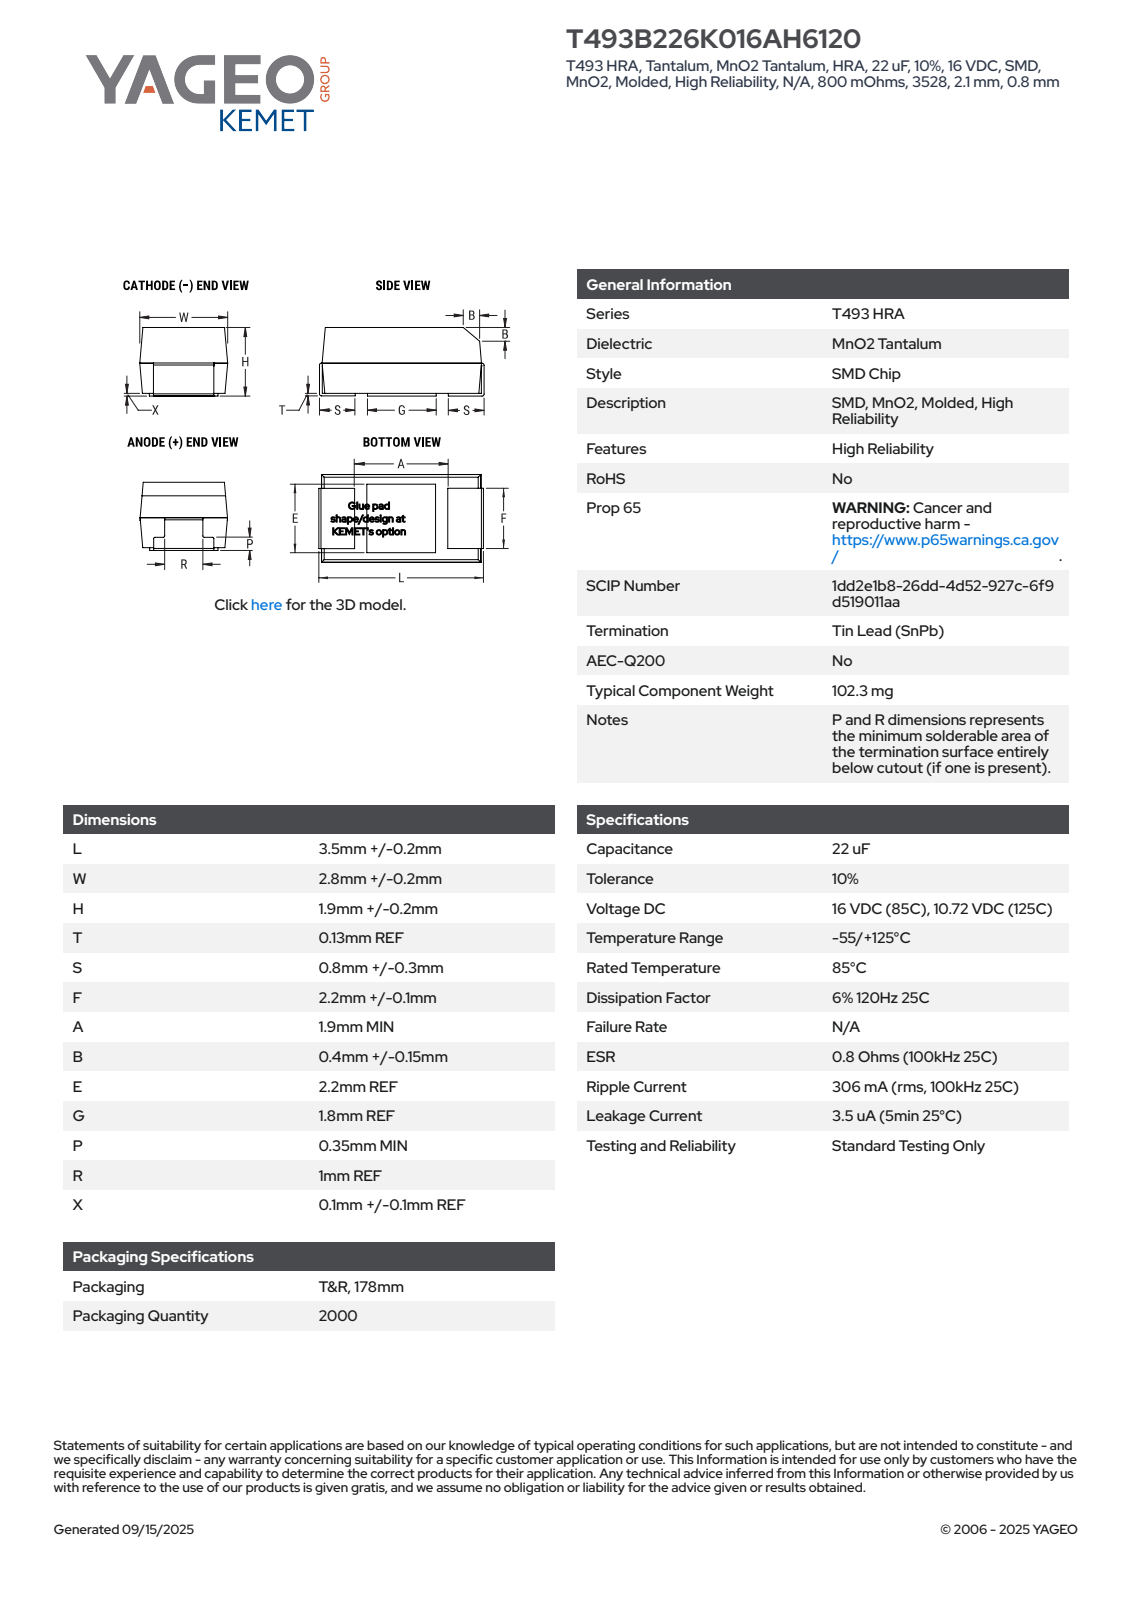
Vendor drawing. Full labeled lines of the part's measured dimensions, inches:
Part name (STEP PRODUCT): CTSM_T496B_3528_L3.7W3H2.1T0.13S0.8F2.3A1.9B0.55E2.2G1.8P0.35R1X0.2
STEP written by: SolidWorks 2014 (AUTOMOTIVE_DESIGN)
Units: inches
Bodies: 4 solids, 98 faces (94 planar, 4 cylindrical, 0 other)
Overall size (bounding box): 0.146 × 0.118 × 0.083
Volume: 0.001 in³ · Surface area: 0.088 in²
Partial cylindrical surfaces — rounded edges, fillets, slot ends (radius × count): R0.004 ×4
Main face-to-face distances: 0.083, 0.117, 0.075, 0.078, 0.141, 0.146, 0.037, 0.032, 0.108, 0.103
